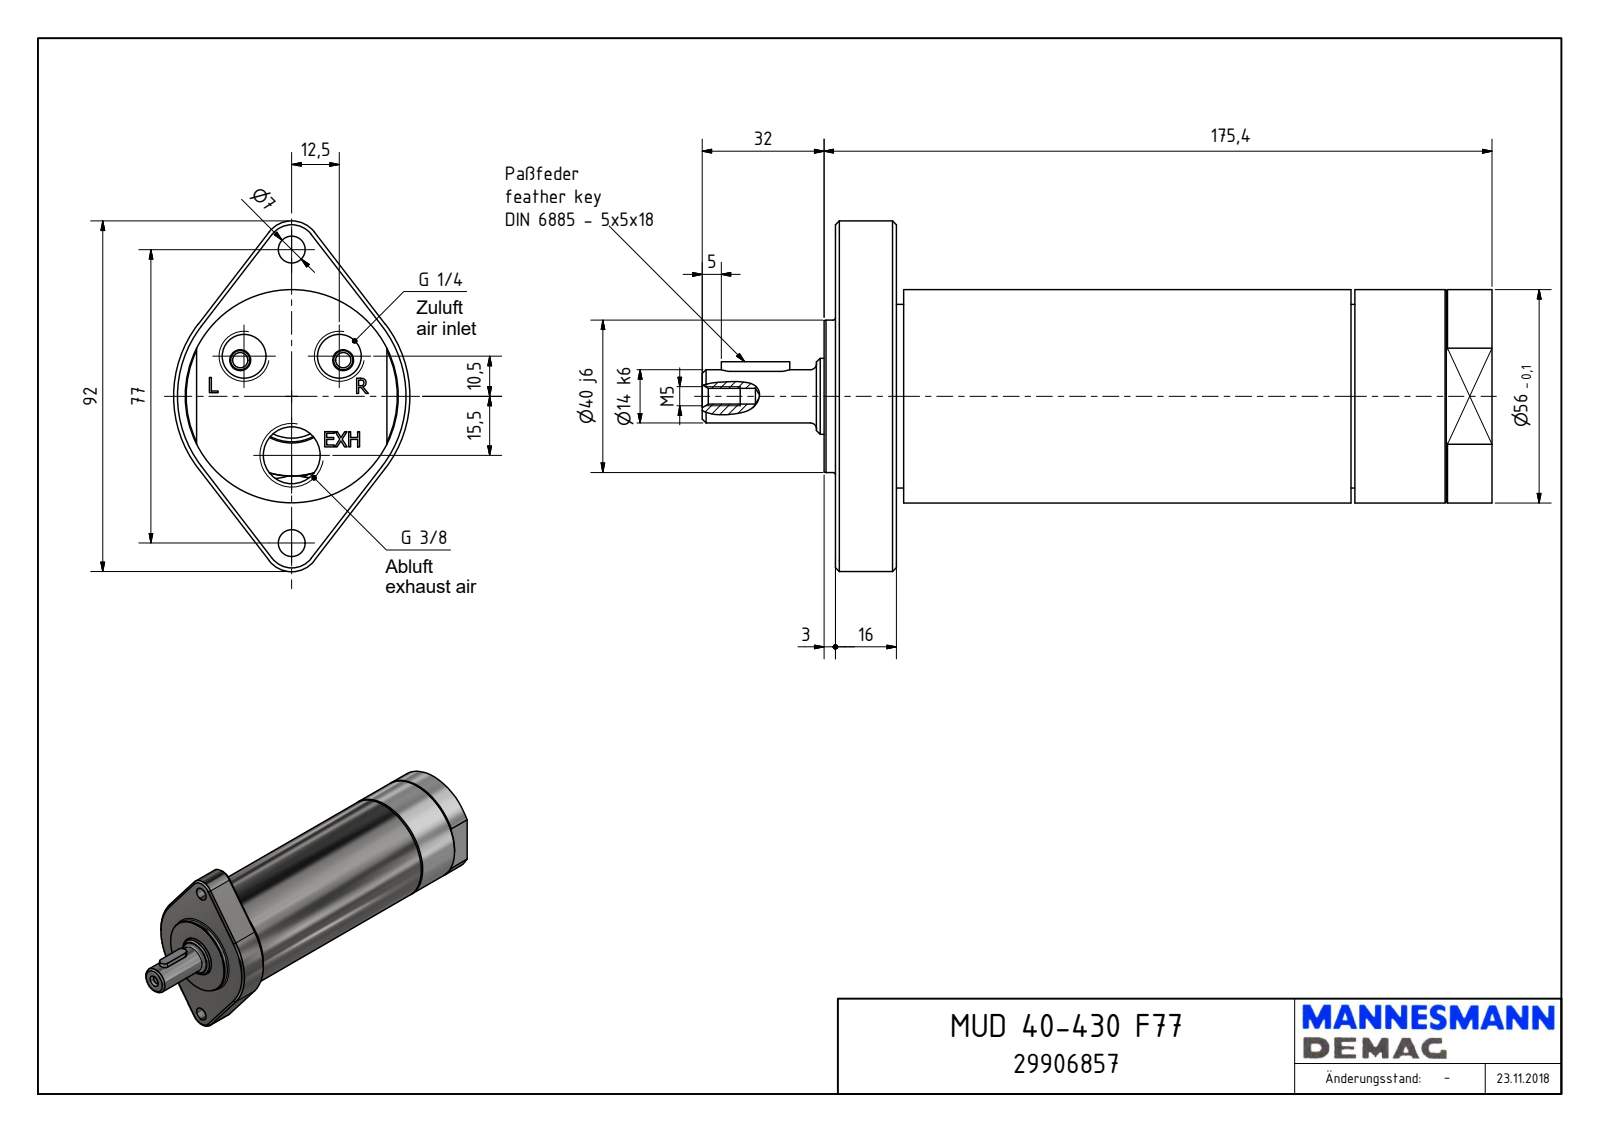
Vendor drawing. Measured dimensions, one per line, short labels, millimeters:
name: MUD 40-430 F77_29906857
written by: Autodesk Inventor 2018 (AUTOMOTIVE_DESIGN)
unit: mm
bodies: 1 solid, 193 faces (105 planar, 36 cylindrical, 52 other)
size: 207.4 × 92 × 62
volume: 444 605 mm³; area: 47 693 mm²
holes: 2× ⌀7, 2× ⌀11.45, 1× ⌀4.13, 1× ⌀14.95, 1× ⌀21, 1× ⌀21.25, 1× ⌀23.54, 1× ⌀26, 1× ⌀48.38
bosses: 1× ⌀56, 1× ⌀48.18, 1× ⌀40, 1× ⌀19.95, 1× ⌀14
rounds: 2× R2.5, 2× R6, 2× R7.5, 1× R20.85, 1× R23, 1× R31
face distances: 172.4, 16, 156.4, 3, 19, 175.4, 20.9, 138.4, 135.4, 119.4
hole spacings: 16.32, 28.85, 30.66, 38.5, 50.57, 15.5, 23, 25
